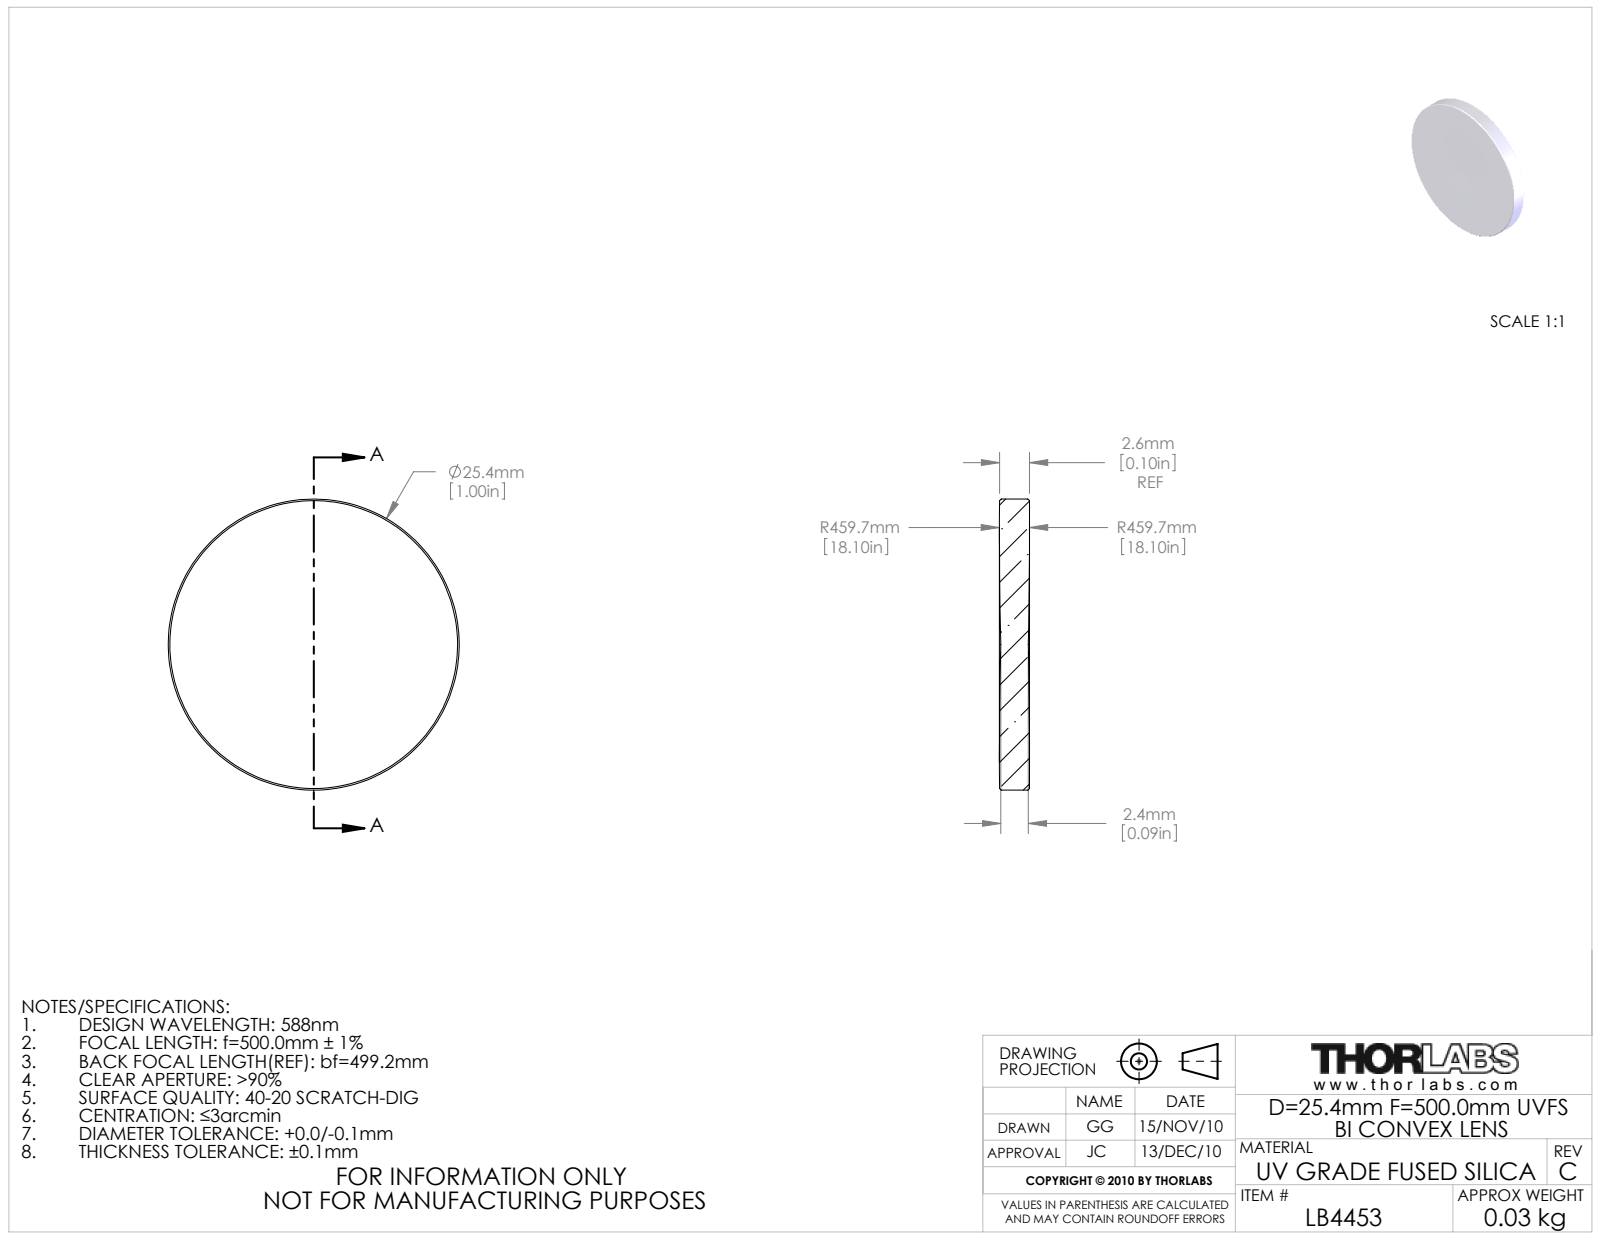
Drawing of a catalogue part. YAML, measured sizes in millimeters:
part_name: "3410-E0W"
step_written_by: "SolidWorks 2009 (AUTOMOTIVE_DESIGN)"
units: millimeters
bodies: {solids: 1, faces: 10, planar: 0, cylindrical: 2, other: 8}
overall_size: [25.4, 25.4, 2.63]
volume: 1316
surface_area: 1209
round_bosses_or_shafts:
  - {diameter: 25.4, count: 1}
